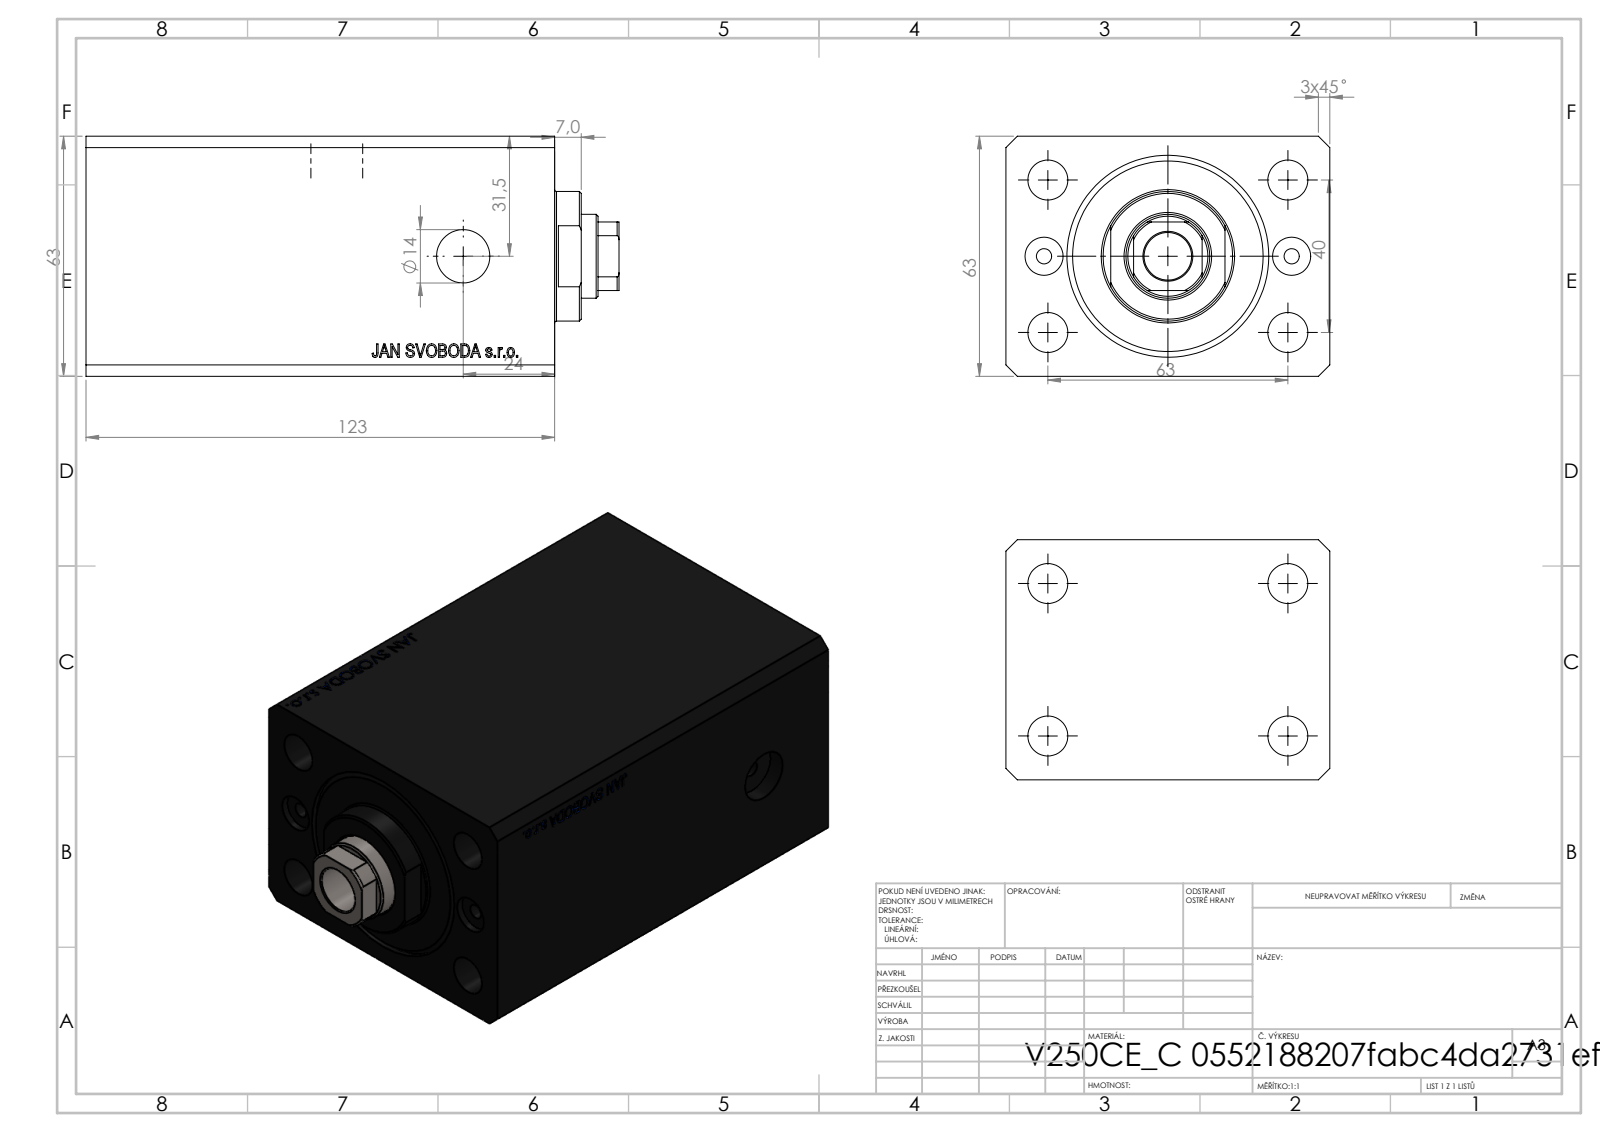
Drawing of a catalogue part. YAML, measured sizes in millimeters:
part_name: "V250CE_VC_C; V250CE_C_Body; V250CE_C_VCP"
step_written_by: "SolidWorks 2019 (CONFIG_CONTROL_DESIGN)"
units: millimeters
bodies: {solids: 3, faces: 864, planar: 428, cylindrical: 44, other: 392}
overall_size: [140, 85, 63]
volume: 573478
surface_area: 102124
round_holes:
  - {diameter: 4, count: 4}
  - {diameter: 10.5, count: 4}
  - {diameter: 10, count: 2}
  - {diameter: 14, count: 2}
  - {diameter: 12.5, count: 1}
  - {diameter: 22, count: 1}
  - {diameter: 40, count: 1}
  - {diameter: 53, count: 1}
round_bosses_or_shafts:
  - {diameter: 34, count: 1}
partial_cylinders:
  - {radius: 10.5, count: 1}
face_to_face_distances: [63, 85, 123, 17, 106, 11.4, 94.6, 111.6, 100.4, 50]
hole_center_spacings: [20.02, 37.31, 67.05, 32.5, 40, 63, 74.63, 65]
